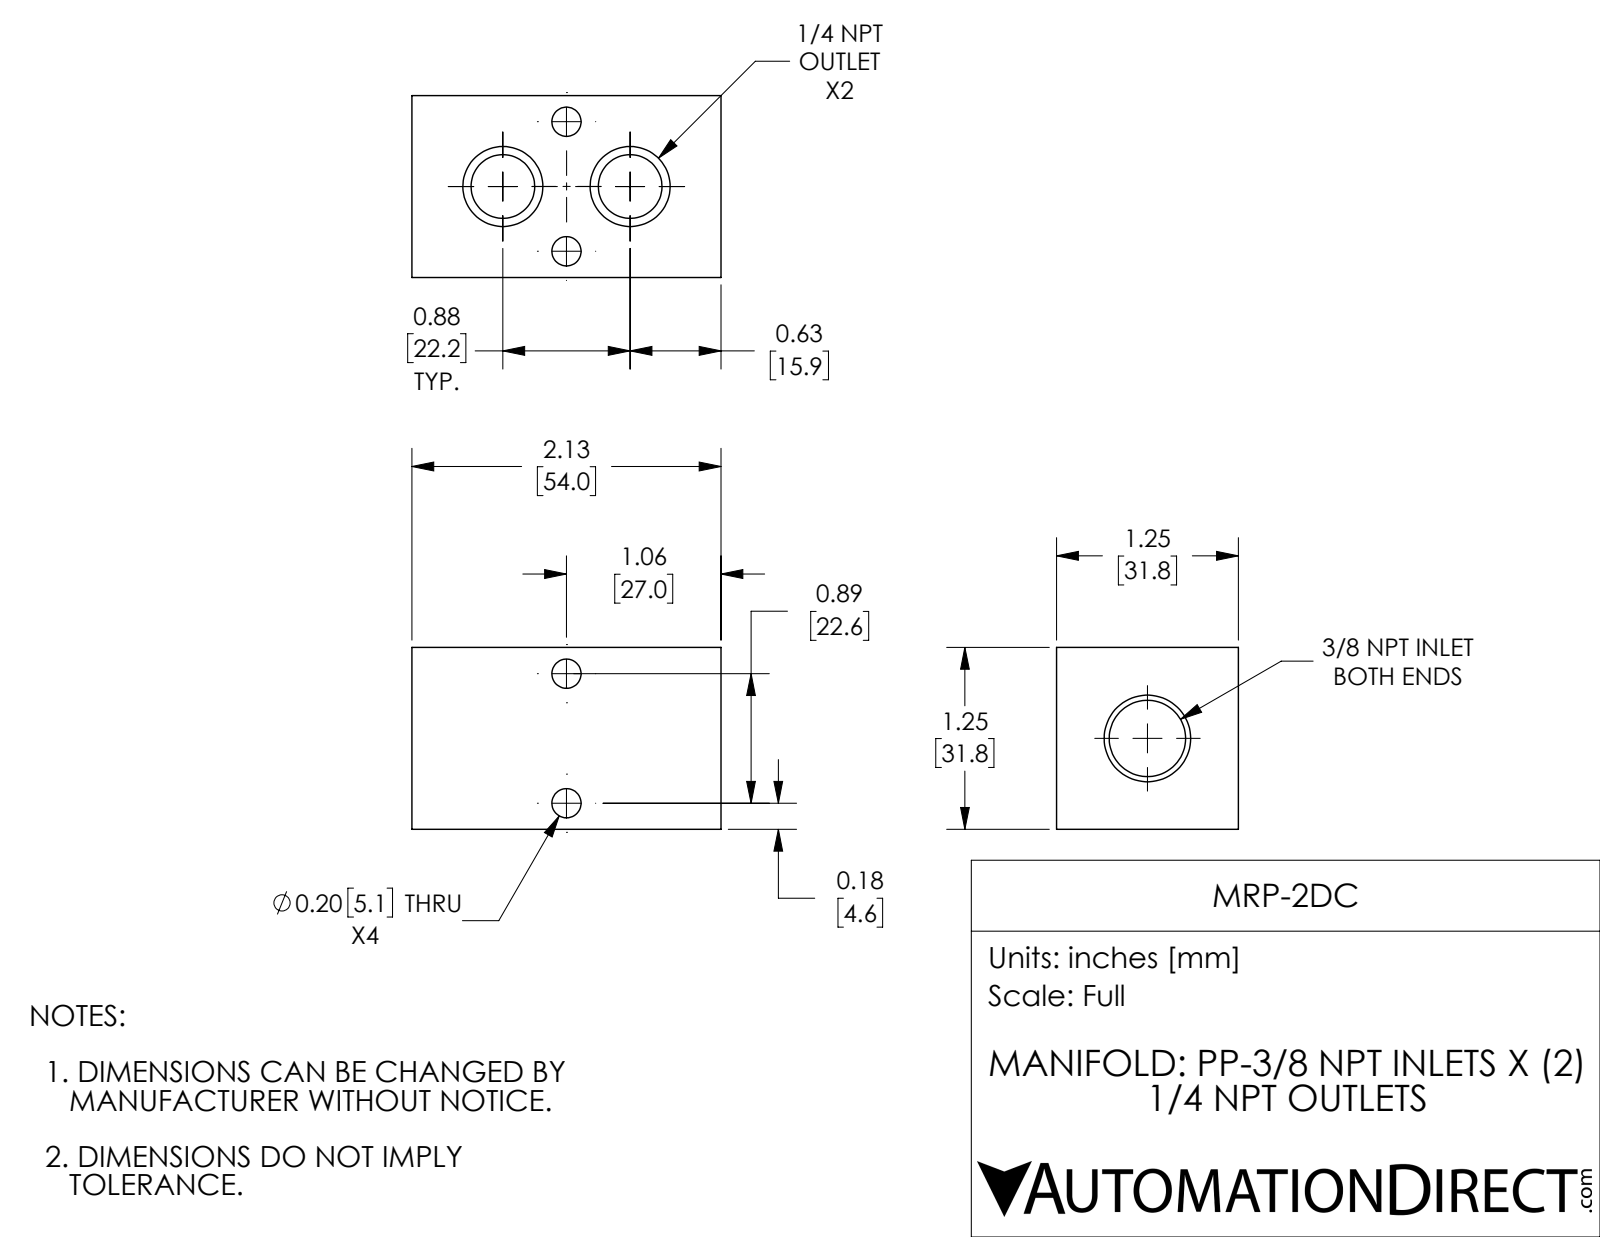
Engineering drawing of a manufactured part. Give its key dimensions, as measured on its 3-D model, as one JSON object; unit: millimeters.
{"part_name": "MRP-2DC", "step_written_by": "SolidWorks 2018 (AUTOMOTIVE_DESIGN)", "units": "millimeters", "bodies": {"solids": 1, "faces": 44, "planar": 6, "cylindrical": 30, "other": 8}, "overall_size": [54, 31.8, 31.8], "volume_mm3": 42610, "surface_area_mm2": 12540, "round_holes": [[5.1, 4], [11.1, 2], [13.3, 1]], "face_to_face_distances": [31.8, 54], "hole_center_spacings": [15.8, 22.6, 22.2]}
